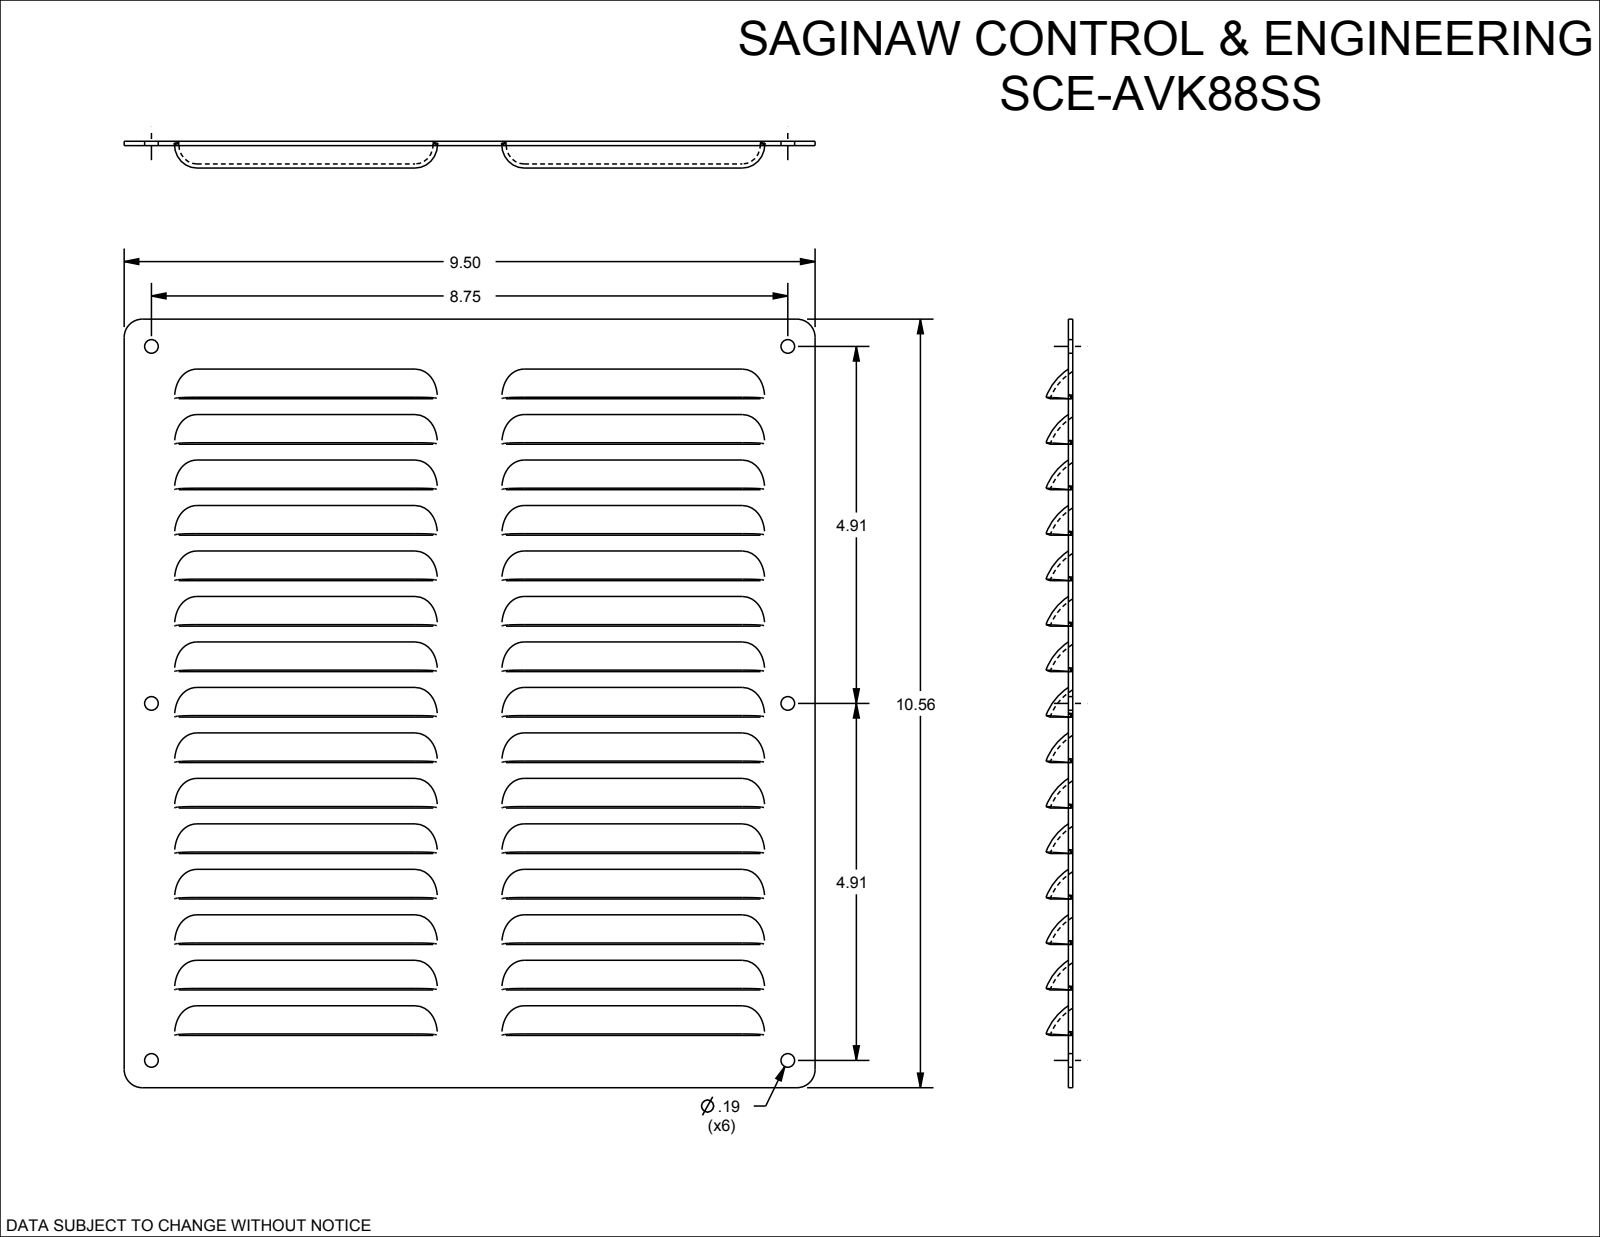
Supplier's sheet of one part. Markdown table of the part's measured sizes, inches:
| quantity | value |
| --- | --- |
| part name | SCE-AVK88SS |
| STEP written by | SolidWorks 2019 (CONFIG_CONTROL_DESIGN) |
| units | inches |
| bodies | 1 solid, 442 faces (66 planar, 76 cylindrical, 300 other) |
| overall size | 10.563 × 9.5 × 0.48 |
| volume | 6.797 in³ |
| surface area | 243 in² |
| round holes (diameter × count) | 0.187 × 6 |
| partial cylindrical surfaces (radius × count) | 0.74 × 15, 0.8 × 15, 0.25 × 4 |
| main face-to-face distances | 0.06, 1.25, 1.171, 2.5, 2.343, 3.75, 3.514, 0.625, 5, 0.625 |
| hole center spacings | 4.906, 10.031, 8.75, 9.813, 13.147 |
